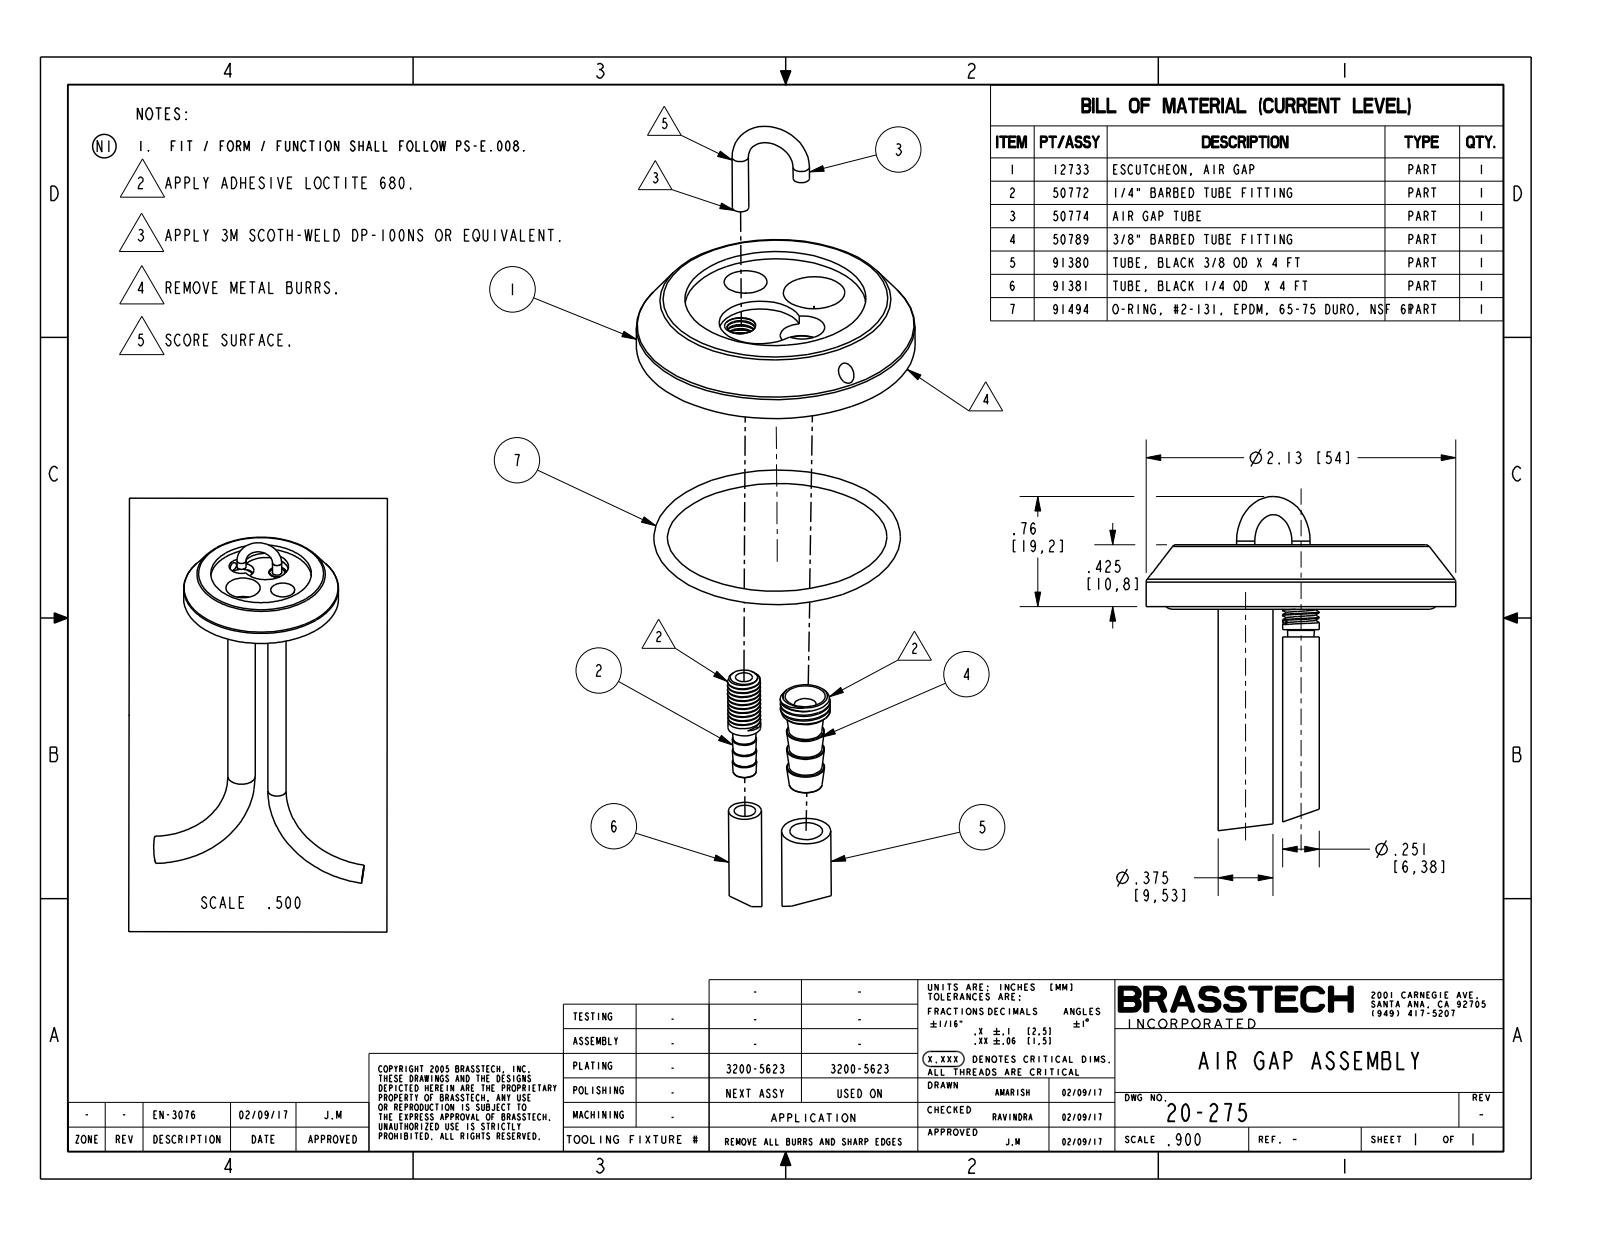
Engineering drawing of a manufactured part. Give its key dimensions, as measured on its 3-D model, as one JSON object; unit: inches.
{"part_name": "12733; 50772; 50774; 50789 (+4 more)", "step_written_by": "CREO PARAMETRIC BY PTC INC, 2018400 (CONFIG_CONTROL_DESIGN)", "units": "inches", "bodies": {"solids": 7, "faces": 268, "planar": 62, "cylindrical": 84, "other": 122}, "overall_size": [5.59, 2.479, 2.218], "volume_in3": 1.542, "surface_area_in2": 39.23, "round_holes": [[0.069, 2], [0.098, 1], [0.125, 1], [0.13, 1], [0.165, 1], [0.166, 1], [0.22, 1], [0.25, 1], [0.328, 1], [0.34, 1], [0.469, 1], [0.625, 1]], "round_bosses_or_shafts": [[0.125, 2], [2.125, 1], [1.685, 1], [0.38, 1], [0.375, 1], [0.251, 1], [0.25, 1]], "face_to_face_distances": [0.375, 0.05, 0.425, 0.31, 0.36, 0.065, 0.085, 0.035, 0.275, 0.34], "hole_center_spacings": [0.517, 0.161, 0.269, 0.31, 0.331, 0.332, 0.35, 0.38]}
